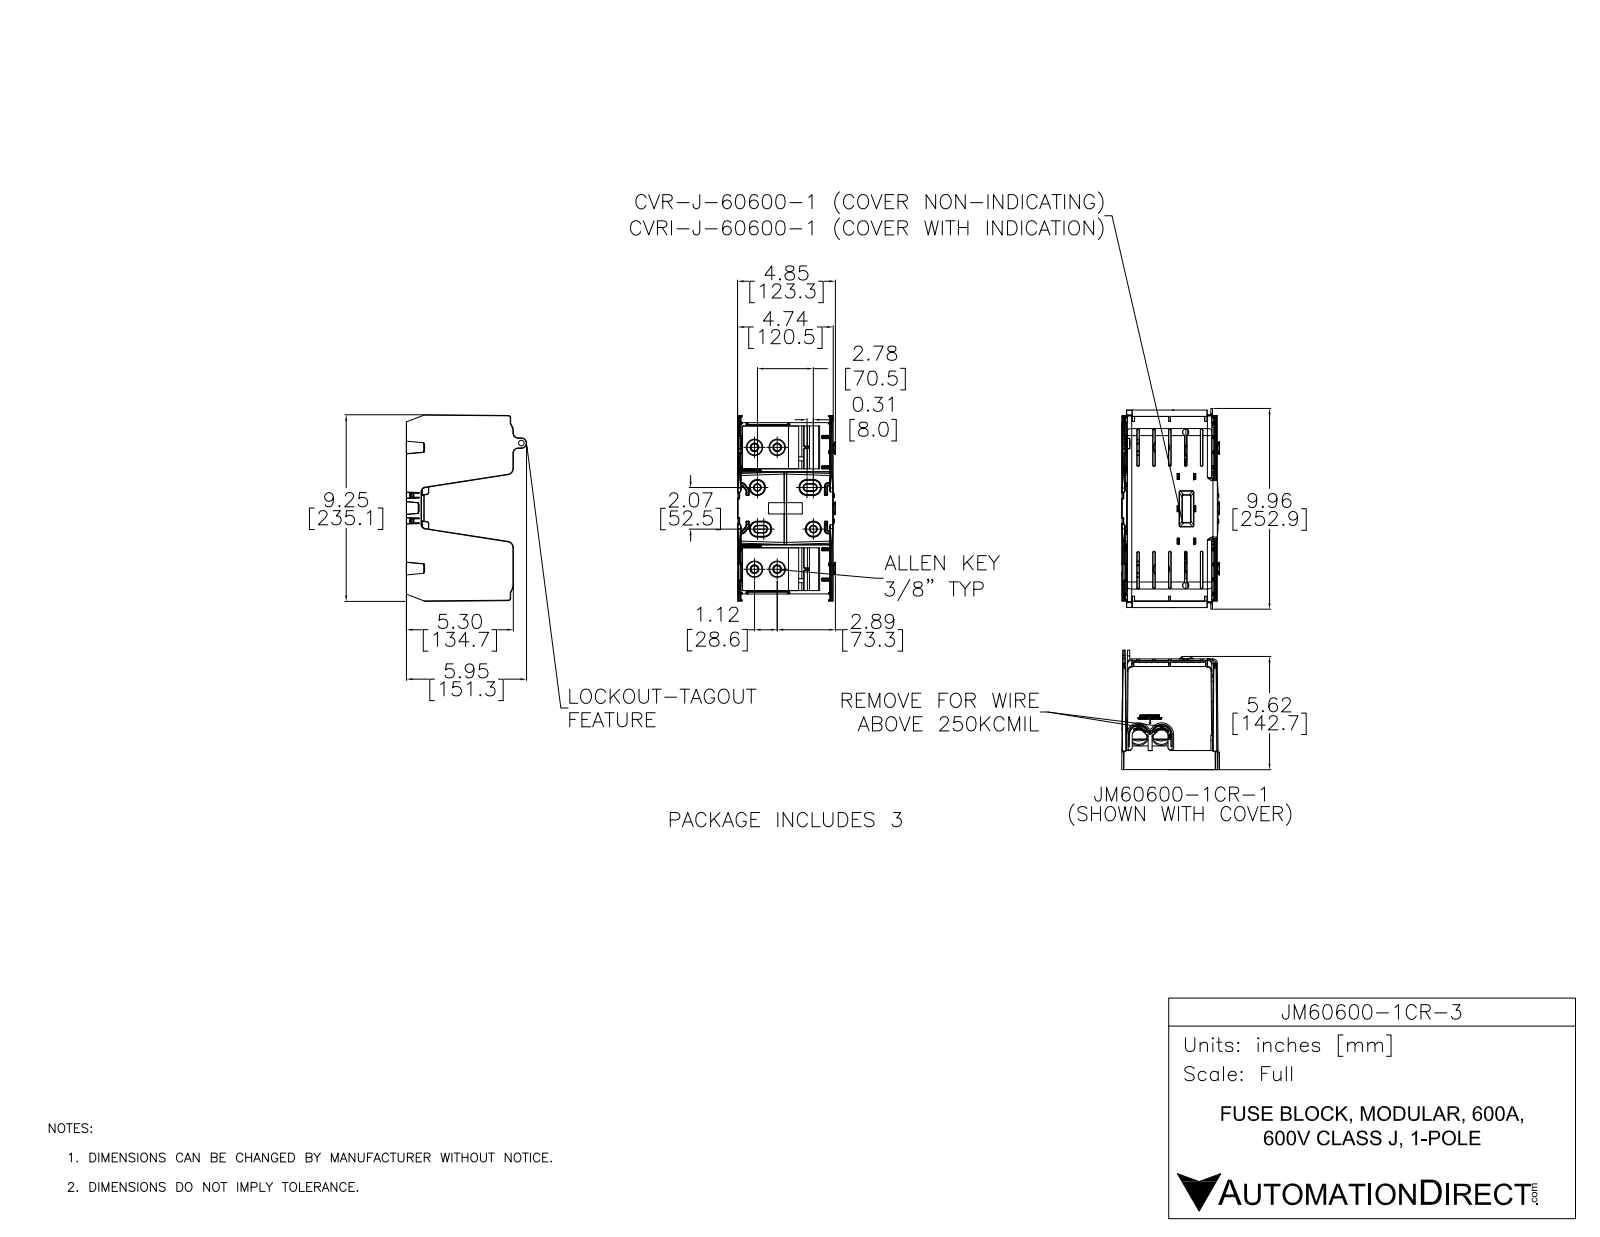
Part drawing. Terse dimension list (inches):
name: JM60600-1CR-3
written by: SolidWorks 2021 (CONFIG_CONTROL_DESIGN)
unit: in
bodies: 0 solids, 3063 faces (984 planar, 1344 cylindrical, 735 other)
size: 14.413 × 9.254 × 5.958
bosses: 11× ⌀0.812, 6× ⌀0.196, 5× ⌀0.875, 2× ⌀0.5, 1× ⌀0.875, 1× ⌀0.812, 1× ⌀0.277
rounds: 364× R0.02, 153× R0.01, 76× R0.02, 54× R0.014, 48× R0.01, 41× R0.014, 27× R0.039, 18× R0.015
face distances: 4.768, 4.601, 9.535, 0.125, 0.167, 4.768, 9.536, 0.048, 0.95, 9.369
